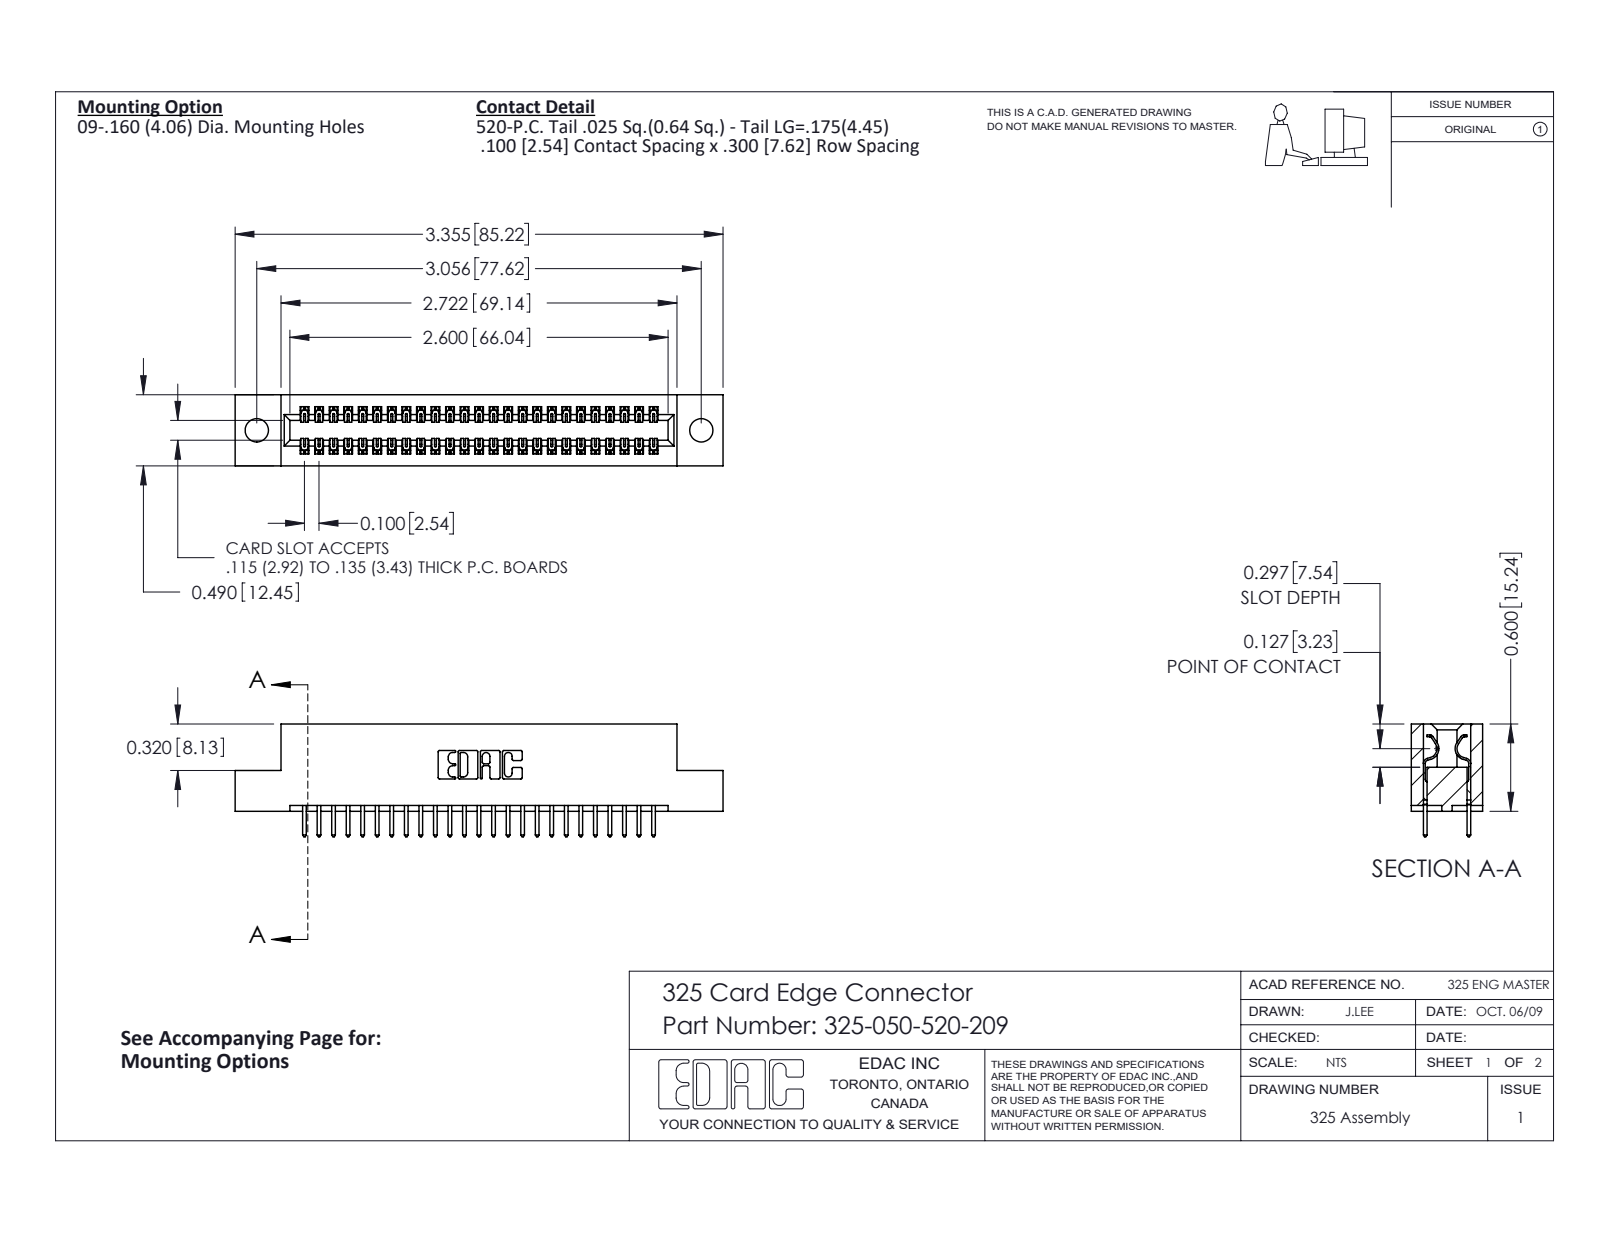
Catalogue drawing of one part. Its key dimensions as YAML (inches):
part_name: "325-050-520-209; 325 Part_.160 TH; 325-292-001_325-293-120"
step_written_by: "SolidWorks 2016 (CONFIG_CONTROL_DESIGN)"
units: inches
bodies: {solids: 51, faces: 2714, planar: 1870, cylindrical: 844, other: 0}
overall_size: [3.355, 0.775, 0.49]
volume: 0.647
surface_area: 19
round_holes:
  - {diameter: 0.16, count: 2}
partial_cylinders:
  - {radius: 0.006, count: 75}
  - {radius: 0.01, count: 50}
  - {radius: 0.01, count: 22}
  - {radius: 0.007, count: 6}
  - {radius: 0.031, count: 6}
  - {radius: 0.026, count: 3}
  - {radius: 0.014, count: 2}
  - {radius: 0.022, count: 2}
face_to_face_distances: [0.083, 0.407, 0.3, 0.49, 0.107, 0.383, 0.025, 0.325, 0.04, 0.275]
hole_center_spacings: [3.056]
